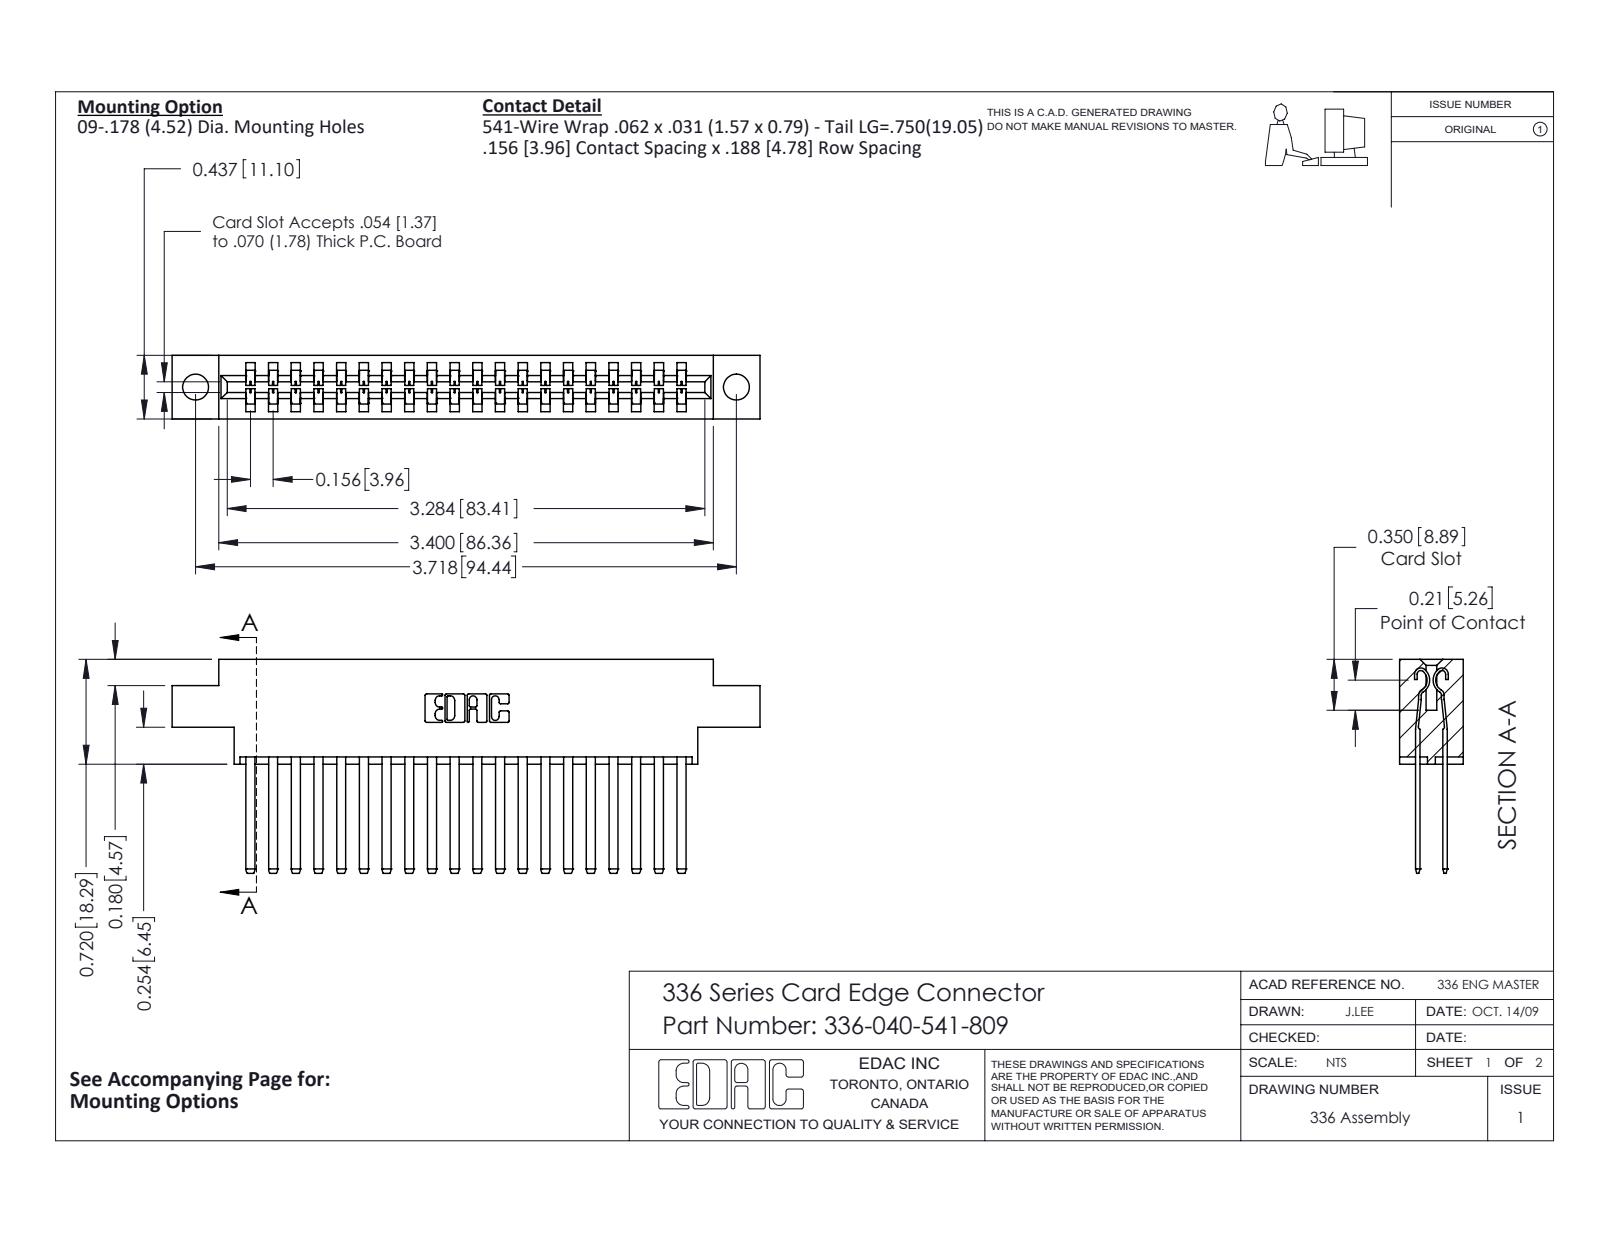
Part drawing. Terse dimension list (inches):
name: 336-040-541-809; 336 Part_Offset - .178 Dia - TH; 336-290-001_336-290-541
written by: SolidWorks 2020 (CONFIG_CONTROL_DESIGN)
unit: in
bodies: 41 solids, 1798 faces (1114 planar, 684 cylindrical, 0 other)
size: 4.041 × 1.47 × 0.437
volume: 0.915 in³; area: 28.96 in²
holes: 2× ⌀0.178
rounds: 80× R0.004, 40× R0.056, 22× R0.01, 6× R0.007, 6× R0.031, 4× R0.022, 4× R0.04, 3× R0.026
face distances: 0.188, 0.328, 0.14, 0.297, 0.109, 0.031, 0.437, 0.033, 0.156, 0.181
hole spacings: 3.718
